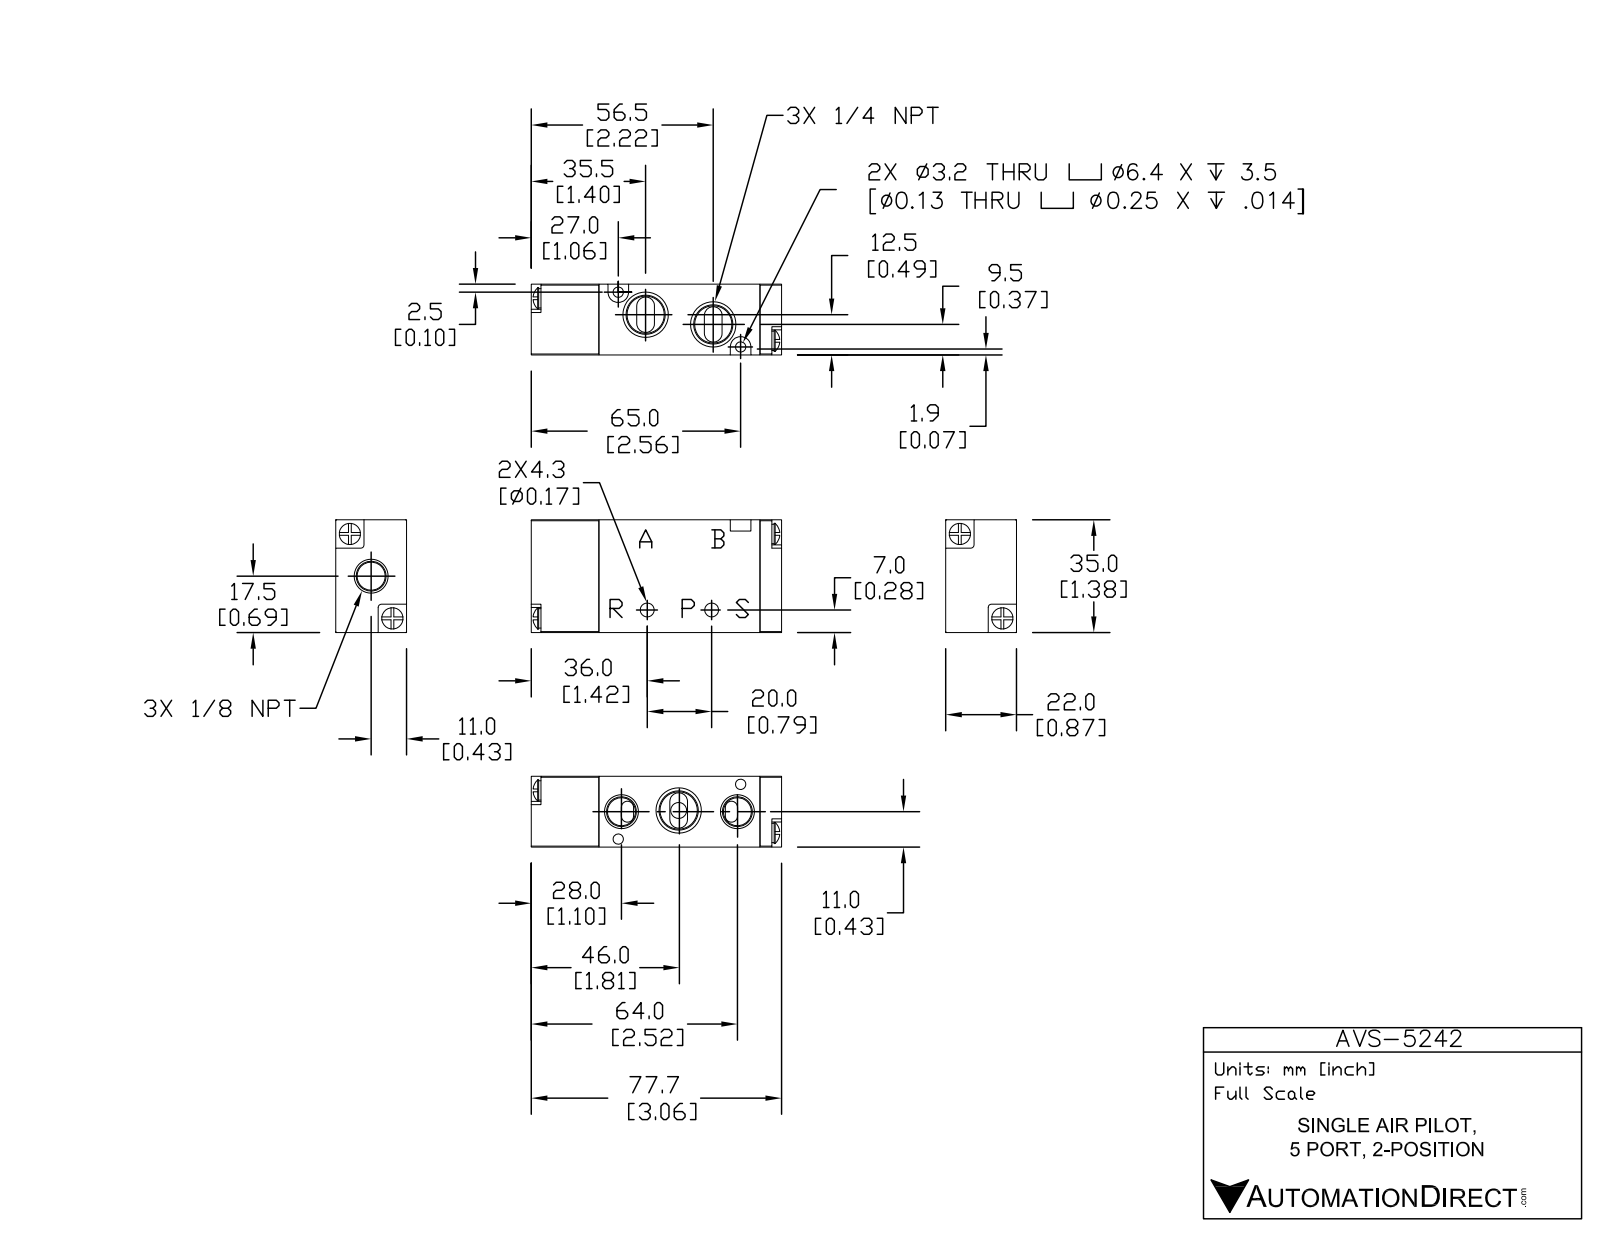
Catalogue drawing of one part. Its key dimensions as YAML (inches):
part_name: "AVS-5242"
step_written_by: "SolidWorks 2015 (CONFIG_CONTROL_DESIGN)"
units: inches
bodies: {solids: 3, faces: 194, planar: 98, cylindrical: 56, other: 40}
overall_size: [3.059, 1.378, 0.866]
volume: 3.141
surface_area: 26.72
round_holes:
  - {diameter: 0.126, count: 2}
  - {diameter: 0.169, count: 2}
  - {diameter: 0.195, count: 1}
round_bosses_or_shafts:
  - {diameter: 0.26, count: 4}
  - {diameter: 0.236, count: 4}
partial_cylinders:
  - {radius: 0.108, count: 6}
  - {radius: 0.012, count: 4}
  - {radius: 0.039, count: 4}
  - {radius: 0.075, count: 4}
  - {radius: 0.126, count: 2}
face_to_face_distances: [0.866, 1.969, 1.378, 0.827, 0.264, 2.232, 3.059, 2.795, 0.551, 0.118]
hole_center_spacings: [0.819, 0.787, 1.639]
